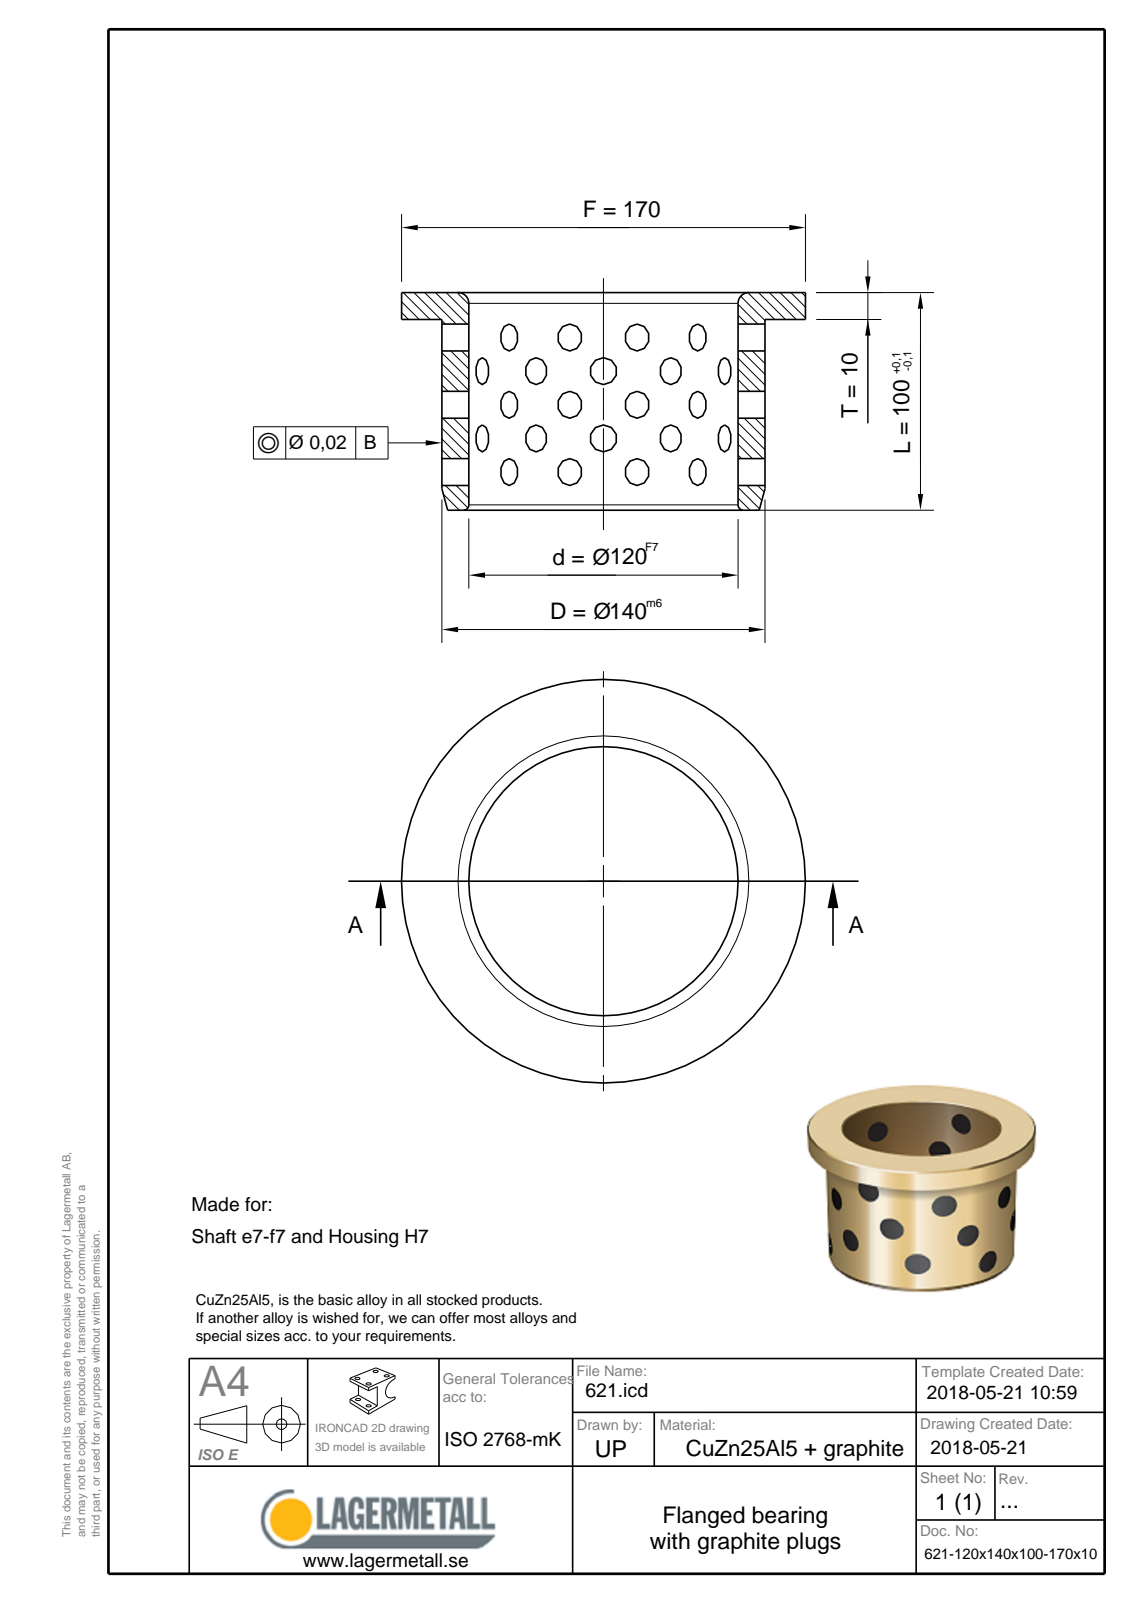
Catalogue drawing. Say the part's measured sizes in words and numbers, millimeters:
The part is named "621-120x140x100-170x10". Its 3-D file was written by "Spatial InterOp 3D (CONFIG_CONTROL_DESIGN)". It is 1 solid with 9 faces: 3 planar, 3 cylindrical and 3 other. Overall it measures 170 by 170 by 100 millimeters. Its volume is 479 462 cubic millimeters and its surface area 104 109 square millimeters. Round holes: 1 of diameter 120. Round bosses or shafts: 1 of diameter 170, 1 of diameter 140. The main face-to-face distances are 10, 90, 100.
